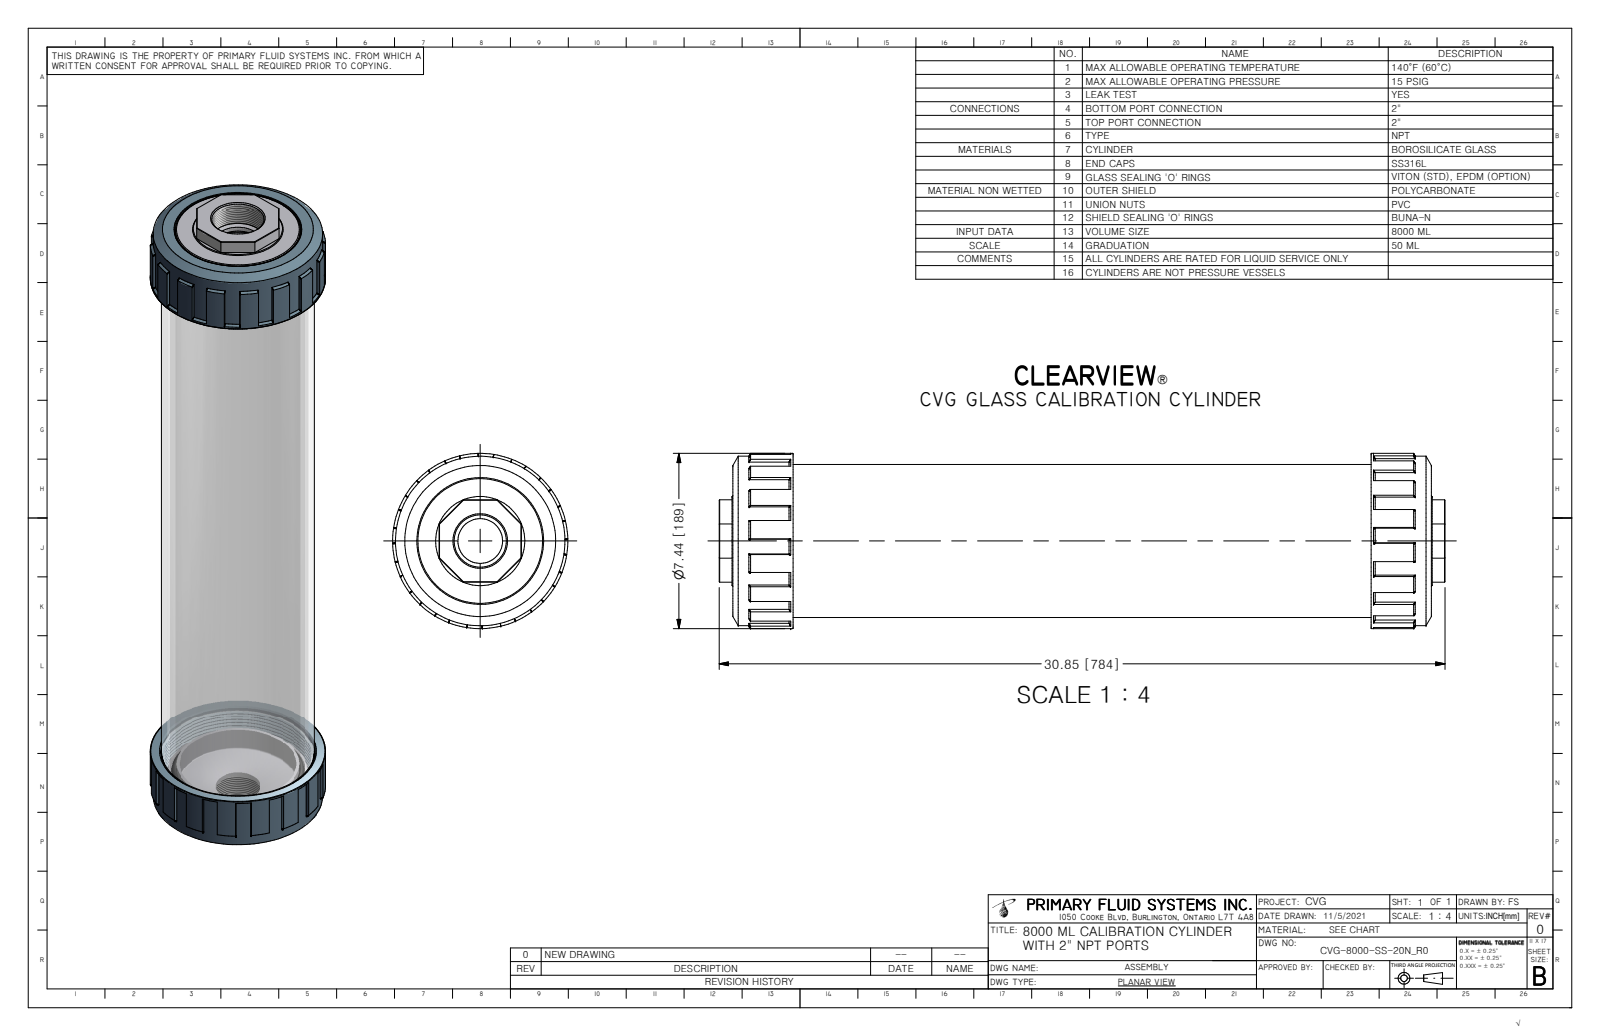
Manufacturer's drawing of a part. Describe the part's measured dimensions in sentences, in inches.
Its 3-D file was written by "Autodesk Inventor 2009 (CONFIG_CONTROL_DESIGN)". It is 1 solid with 355 faces: 132 planar, 81 cylindrical and 142 other. Overall it measures 30.85 by 7.445 by 7.445 inches. Its volume is 71.94 cubic inches and its surface area 2 694 square inches. Round holes: 1 of diameter 1.9, 1 of diameter 2.219, 1 of diameter 4.98, 1 of diameter 5.315, 1 of diameter 5.386, 1 of diameter 5.709, 1 of diameter 5.76, 1 of diameter 5.97, 1 of diameter 6, 1 of diameter 6.535. Round bosses or shafts: 1 of diameter 7.445, 1 of diameter 7.201, 1 of diameter 6.5, 1 of diameter 6.496, 1 of diameter 6.26, 1 of diameter 6.25, 1 of diameter 5.3, 1 of diameter 5.236. Partial cylindrical surfaces (rounded edges, fillets, slot ends): 2 of radius 0.335, 2 of radius 3.38. The main face-to-face distances are 29.69, 2.559, 27.131, 0.58, 3.139, 27.711, 30.27, 24.572, 30.85, 1.4.
